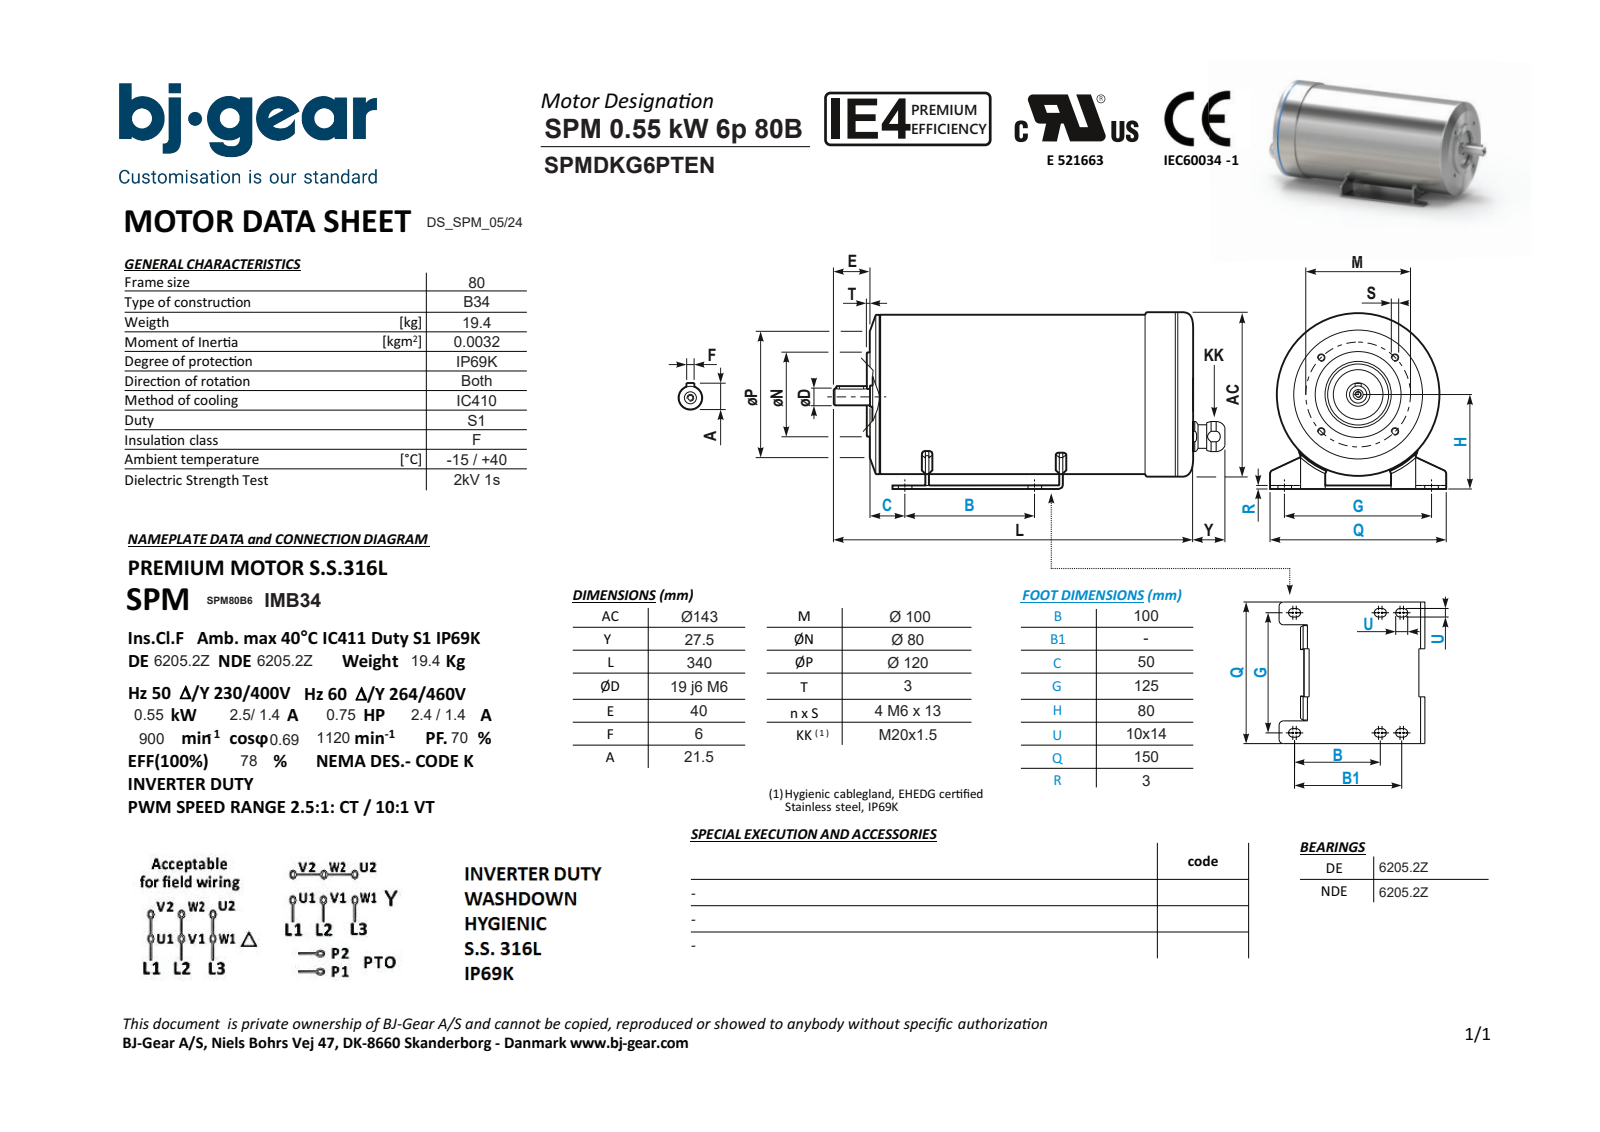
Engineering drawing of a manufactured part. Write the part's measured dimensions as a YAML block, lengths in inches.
part_name: "SPMDKH2PTENN4KSA1-N---NNN; SPMDKH2JTENN4KSA1-N---NNN; SPM809022"
step_written_by: "Solid Edge (AUTOMOTIVE_DESIGN)"
units: inches
bodies: {solids: 2, faces: 157, planar: 66, cylindrical: 66, other: 25}
overall_size: [14.469, 5.965, 5.906]
volume: 282.6
surface_area: 328.2
round_holes:
  - {diameter: 0.194, count: 5}
  - {diameter: 0.252, count: 1}
  - {diameter: 0.276, count: 1}
  - {diameter: 0.528, count: 1}
  - {diameter: 2.677, count: 1}
  - {diameter: 5.472, count: 1}
round_bosses_or_shafts:
  - {diameter: 5.63, count: 1}
  - {diameter: 5.629, count: 1}
  - {diameter: 5.472, count: 1}
  - {diameter: 3.15, count: 1}
  - {diameter: 0.984, count: 1}
  - {diameter: 0.787, count: 1}
  - {diameter: 0.748, count: 1}
partial_cylinders:
  - {radius: 0.197, count: 12}
  - {radius: 0.118, count: 8}
  - {radius: 0.039, count: 4}
  - {radius: 0.157, count: 2}
  - {radius: 0.504, count: 1}
face_to_face_distances: [0.118, 11.811, 0.236, 11.575, 6.969, 2.48, 6.732, 6.85, 4.843, 4.961]
hole_center_spacings: [1.969, 2.784, 1.396, 3.206, 3.937, 1.496]
